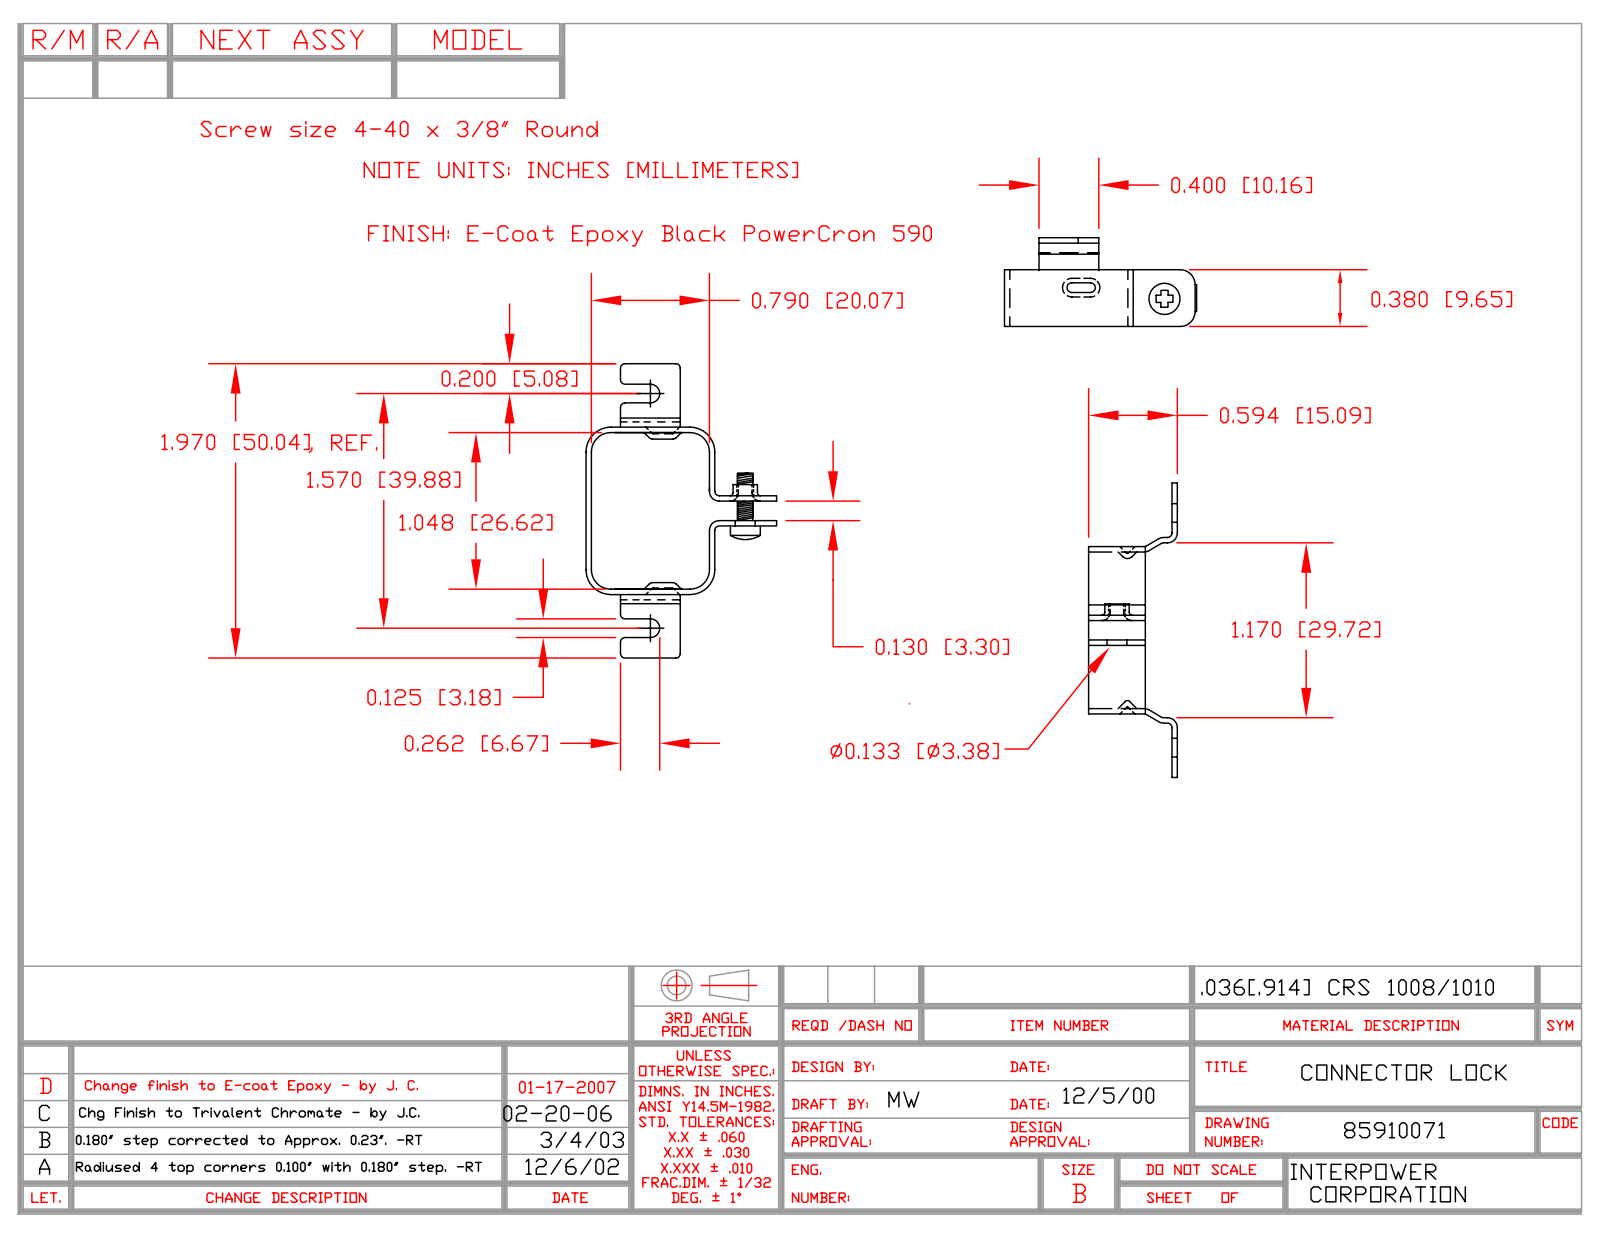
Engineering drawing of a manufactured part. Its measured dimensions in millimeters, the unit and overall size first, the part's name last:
Units: millimetres
Overall size (bounding box): 50.04 × 32.67 × 15.09
Round holes (diameter × count): ⌀2.84 ×1, ⌀3.38 ×1
Round bosses / shafts (diameter × count): ⌀3.35 ×1
Partial cylindrical surfaces — rounded edges, fillets, slot ends (radius × count): R0.76 ×10, R0.91 ×10, R1.83 ×6, R3.3 ×4, R4.22 ×4, R1.59 ×2, R1.68 ×2, R2.36 ×2
Main face-to-face distances: 0.91, 0.92, 11.66, 15.88, 14.96, 16.79, 15.87, 20.98, 21.9, 20.07
Volume: 1 175 mm³ · Surface area: 2 889 mm²
Bodies: 1 solid, 127 faces (59 planar, 52 cylindrical, 16 other)
Part name (STEP PRODUCT): 85910071_R1_C13_Connector-Lock_Black_10-16-12
STEP written by: OneSpace Designer 14.50 18-Oct-2006 (C) CoCreate Software GmbH (AUTOMOTIVE_DESIGN)
